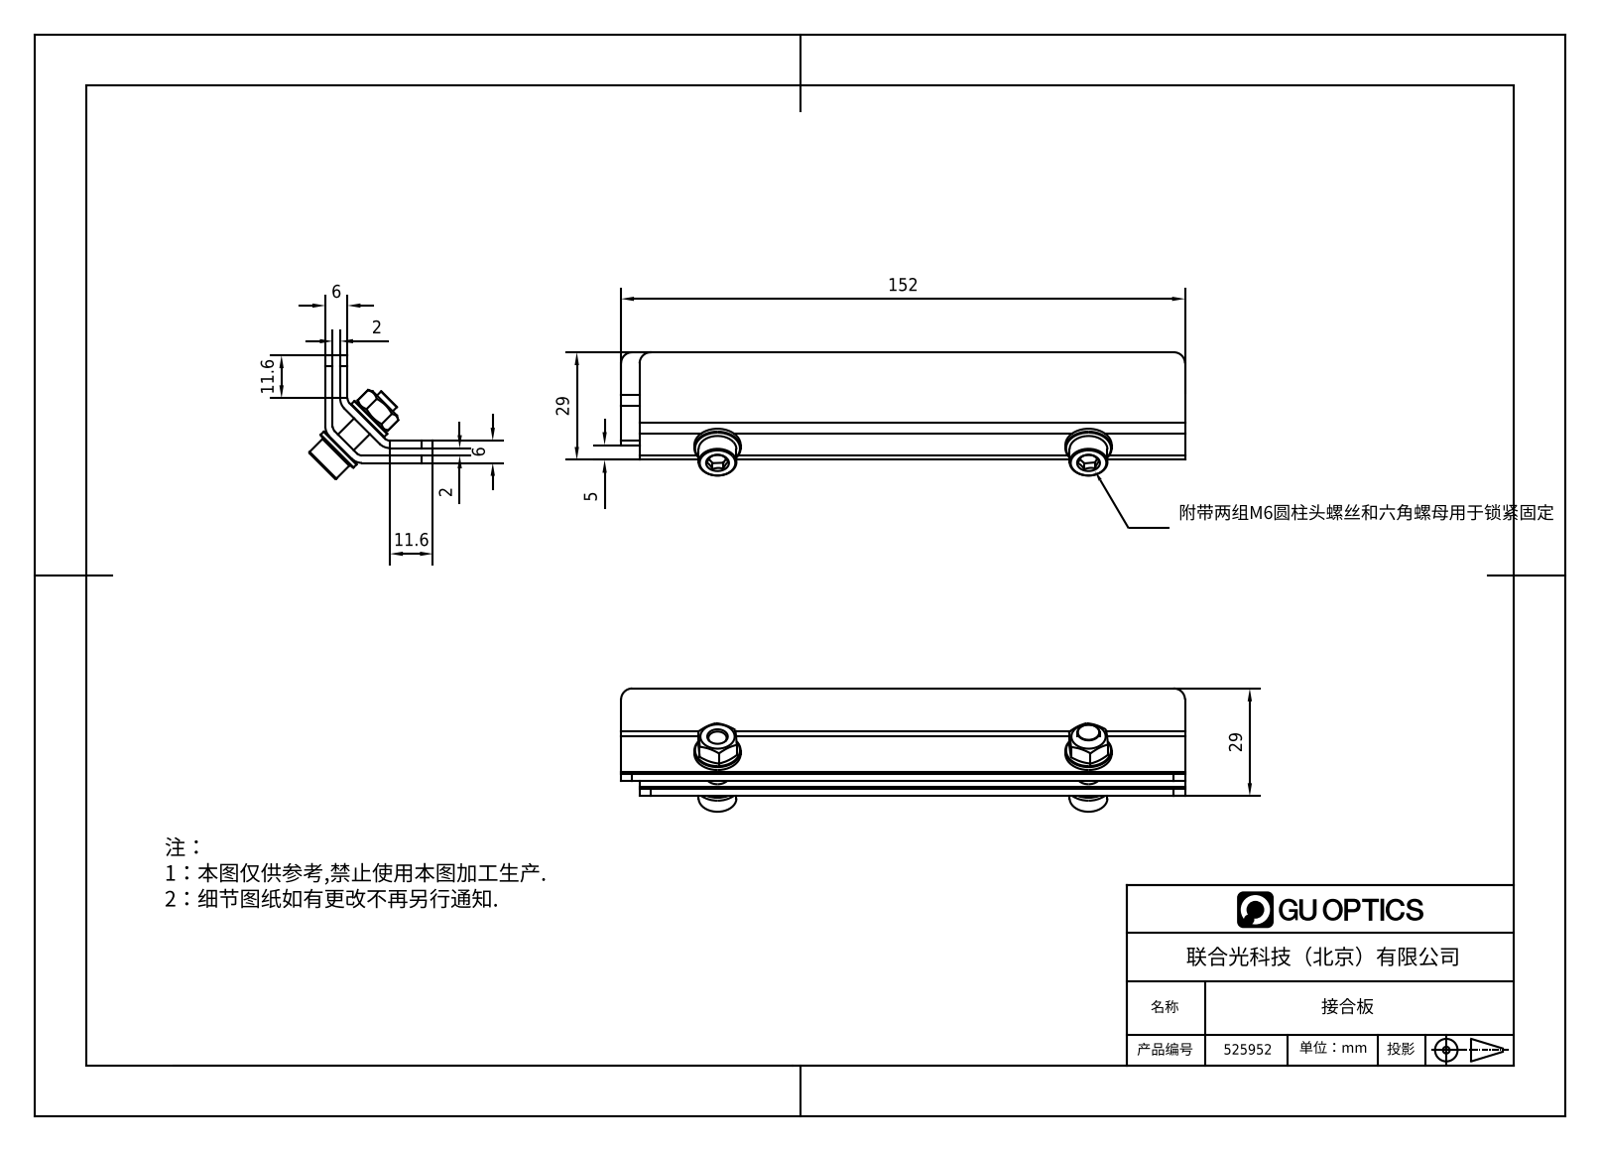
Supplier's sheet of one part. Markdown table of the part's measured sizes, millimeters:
| quantity | value |
| --- | --- |
| part name | 525952 |
| STEP written by | SolidWorks 2020 (CONFIG_CONTROL_DESIGN) |
| units | millimeters |
| bodies | 10 solids, 130 faces (64 planar, 34 cylindrical, 32 other) |
| overall size | 152 × 33.31 × 33.31 |
| volume | 30 308 mm³ |
| surface area | 32 192 mm² |
| round holes (diameter × count) | 6.4 × 2, 6.6 × 2, 4.92 × 1, 4.92 × 1 |
| round bosses / shafts (diameter × count) | 12.5 × 2, 10.2 × 2, 6 × 2 |
| partial cylindrical surfaces (radius × count) | 3 × 6, 2 × 4, 4 × 4 |
| main face-to-face distances | 2, 4, 6, 8.16, 10.16, 23, 6.16, 25, 27, 29 |
| hole center spacings | 100 |
